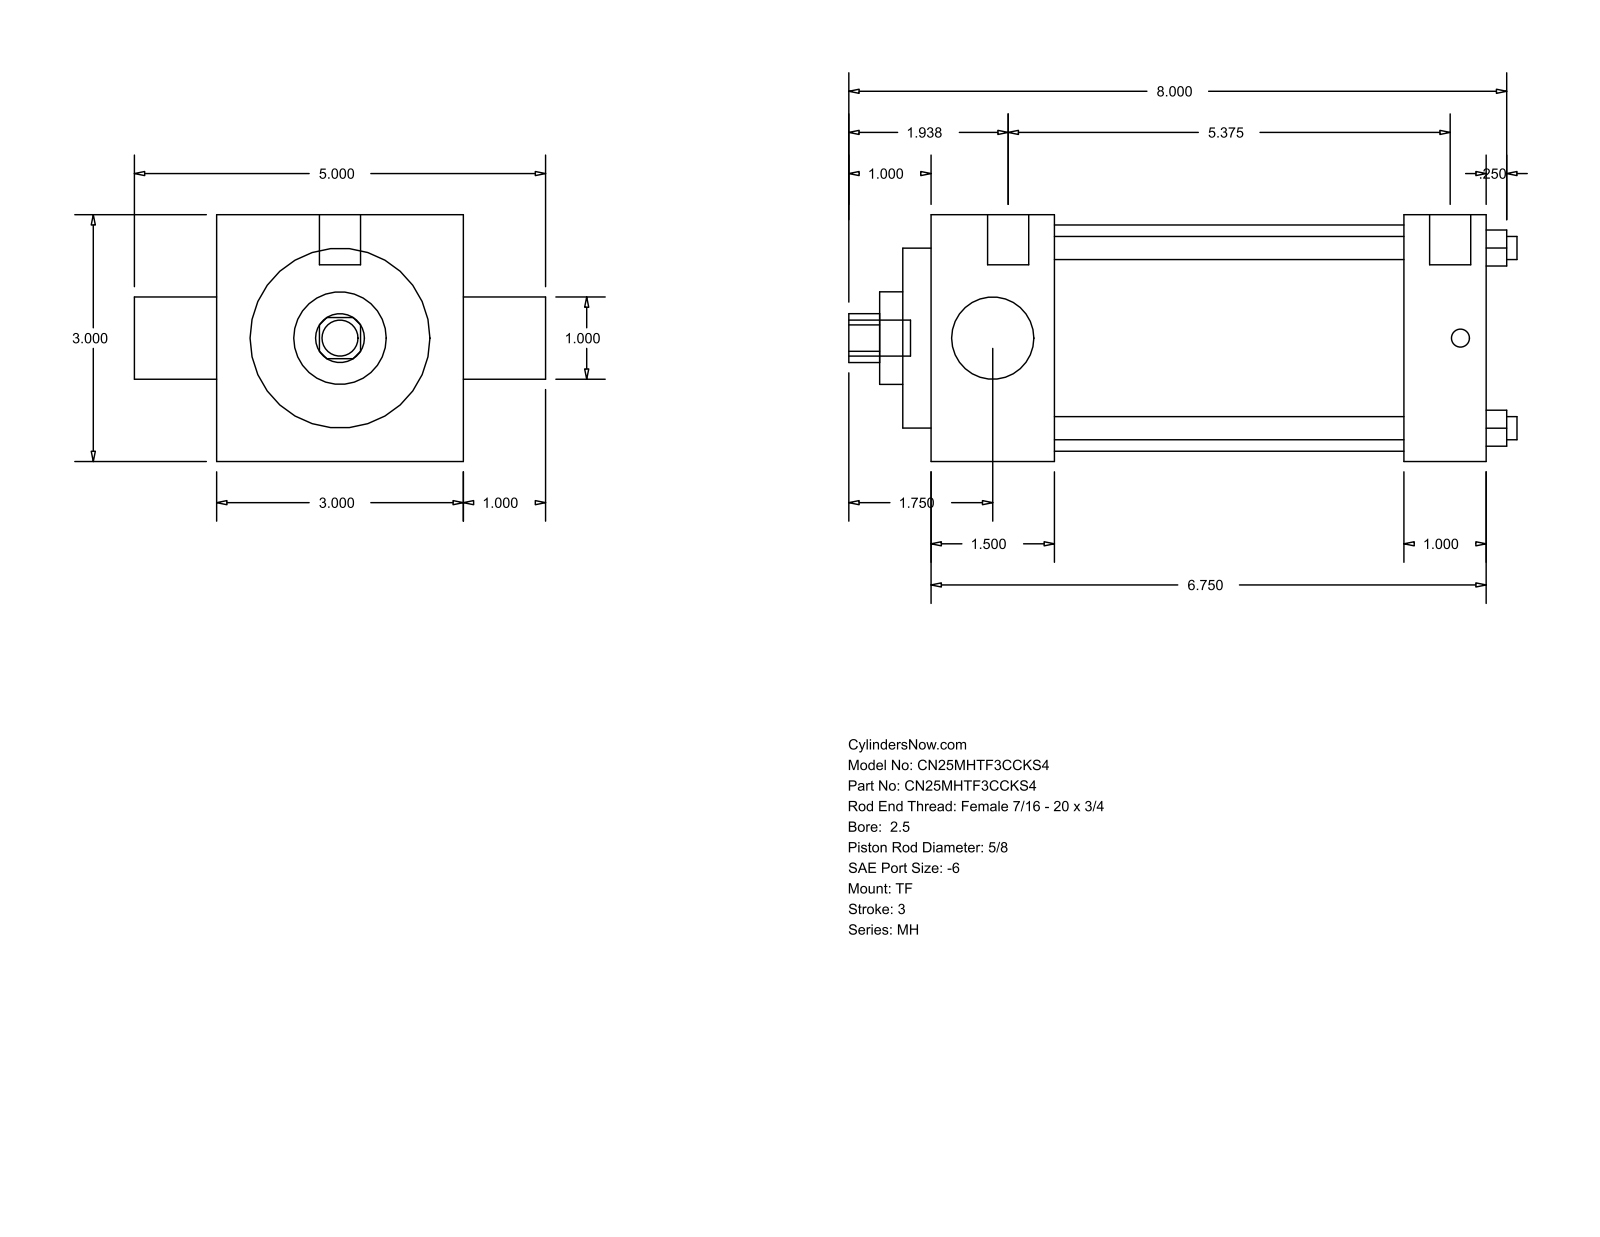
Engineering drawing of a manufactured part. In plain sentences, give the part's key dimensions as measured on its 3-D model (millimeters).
The part is named "MH_TF__0250_0.625". Its 3-D file was written by "GSSL Pune (CONFIG_CONTROL_DESIGN)". It is 0 solids with 86 faces: 61 planar, 25 cylindrical and 0 other. Overall it measures 206.38 by 127 by 76.2 millimeters. Round holes: 4 of diameter 7.14, 1 of diameter 15.88, 1 of diameter 25.4, 1 of diameter 28.57, 1 of diameter 55.55, 1 of diameter 69.85. Round bosses or shafts: 3 of diameter 5.56, 2 of diameter 12.7, 1 of diameter 11.11. Partial cylindrical surfaces (rounded edges, fillets, slot ends): 1 of radius 7.54. The main face-to-face distances are 76.2, 171.45, 25.4, 38.1, 133.35, 146.05, 107.95, 8.73, 46.83, 154.78. The hole center spacings are 39.33, 55.62, 78.66.
